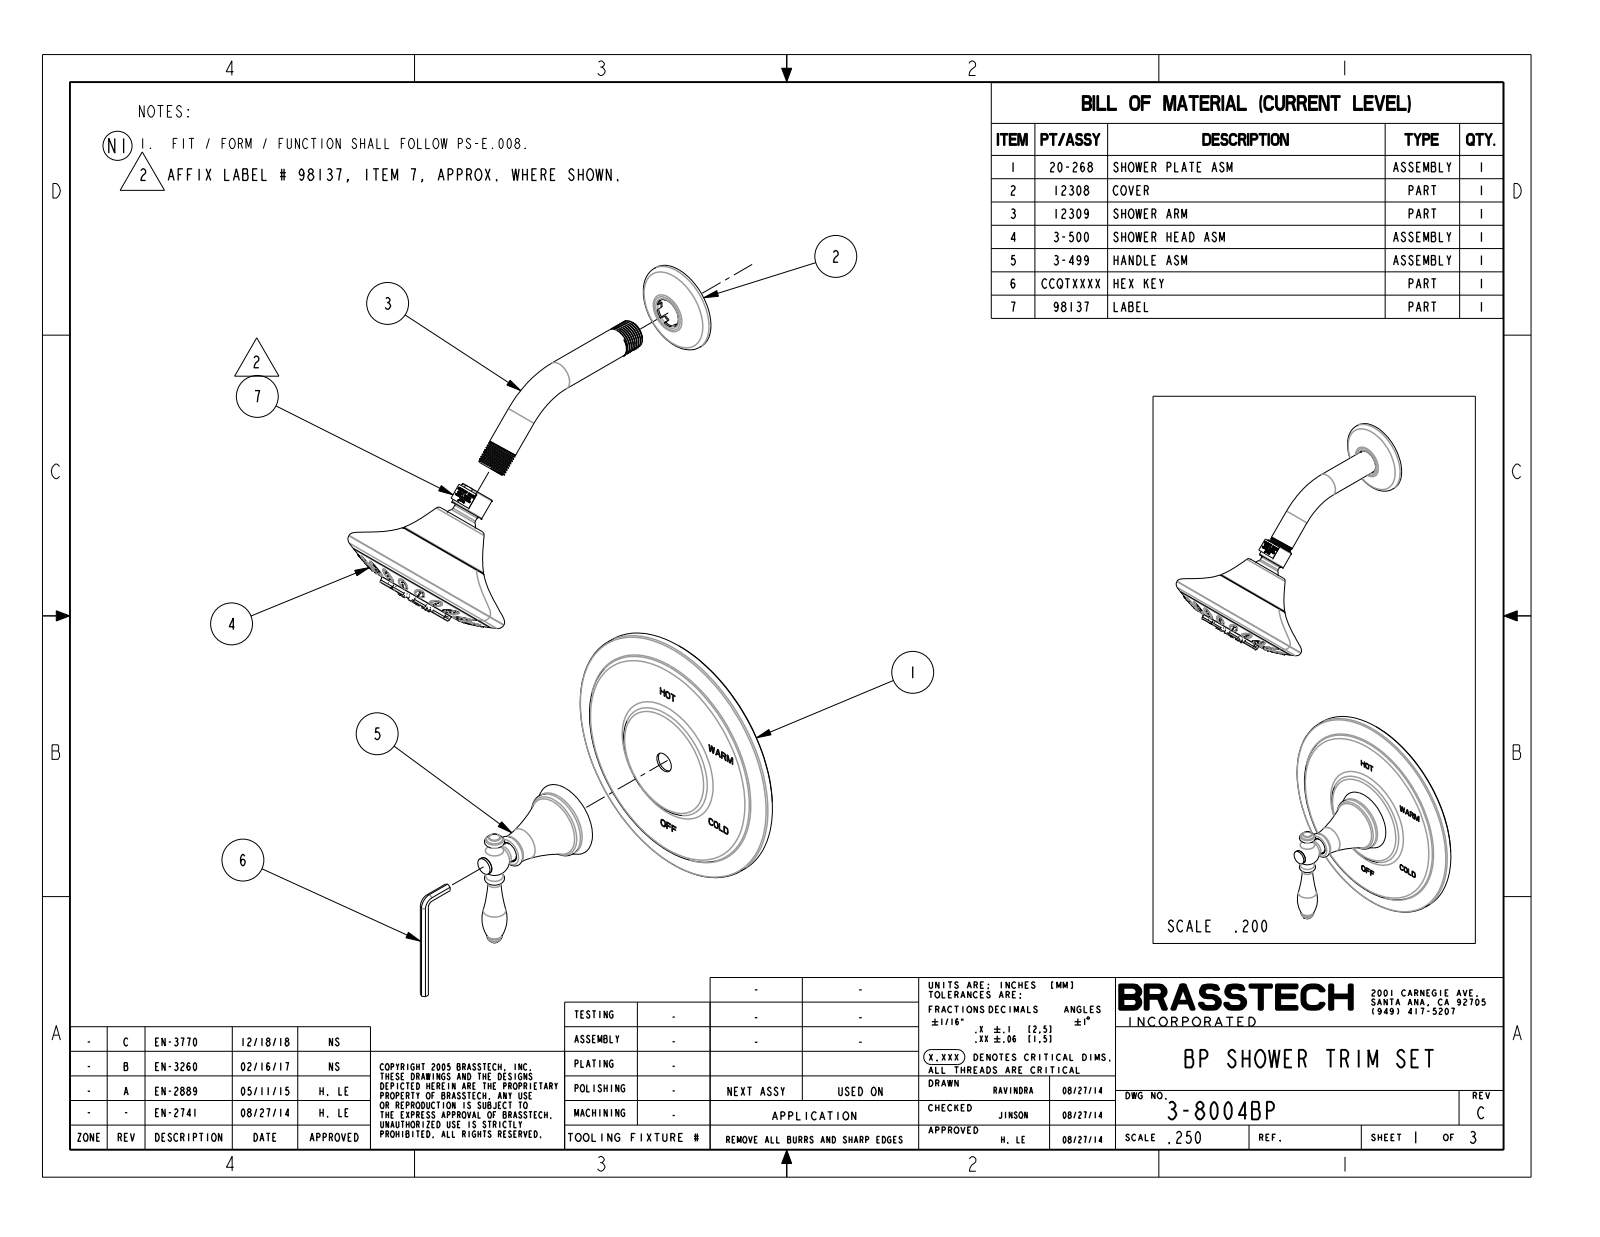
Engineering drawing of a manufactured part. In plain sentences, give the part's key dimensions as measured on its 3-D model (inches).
The part is named "NCIP-027_AF0; PRT0010_1_AF0; 2-961_AF0_ASM; 12308_AF0 (+8 more)". Its 3-D file was written by "PRO/ENGINEER BY PARAMETRIC TECHNOLOGY CORPORATION, 2013150 (CONFIG_CONTROL_DESIGN)". It is 22 solids with 4231 faces: 1250 planar, 940 cylindrical and 2041 other. Overall it measures 19.891 by 8.513 by 7.283 inches. Its volume is 15.52 cubic inches and its surface area 438.2 square inches. Round holes: 13 of diameter 0.079, 12 of diameter 0.063, 9 of diameter 0.118, 8 of diameter 0.213, 8 of diameter 0.268, 8 of diameter 0.37, 5 of diameter 0.236, 2 of diameter 0.535, 2 of diameter 0.685, 1 of diameter 0.156, 1 of diameter 0.181, 1 of diameter 0.197. Round bosses or shafts: 8 of diameter 0.362, 8 of diameter 0.165, 8 of diameter 0.079, 5 of diameter 0.236, 5 of diameter 0.197, 2 of diameter 0.811, 1 of diameter 7.283, 1 of diameter 4.921. Partial cylindrical surfaces (rounded edges, fillets, slot ends): 58 of radius 0.012, 30 of radius 0.004, 20 of radius 0.032, 20 of radius 6.082, 18 of radius 0.02, 18 of radius 0.03, 15 of radius 0.015, 14 of radius 0.063. The main face-to-face distances are 0.059, 0.139, 0.198, 0.571, 0.512, 0.372, 0.431, 0.08, 0.233, 0.314. The hole center spacings are 0.925, 0.984, 1.673, 0.453, 1.873, 1.062, 0.377, 1.588.
